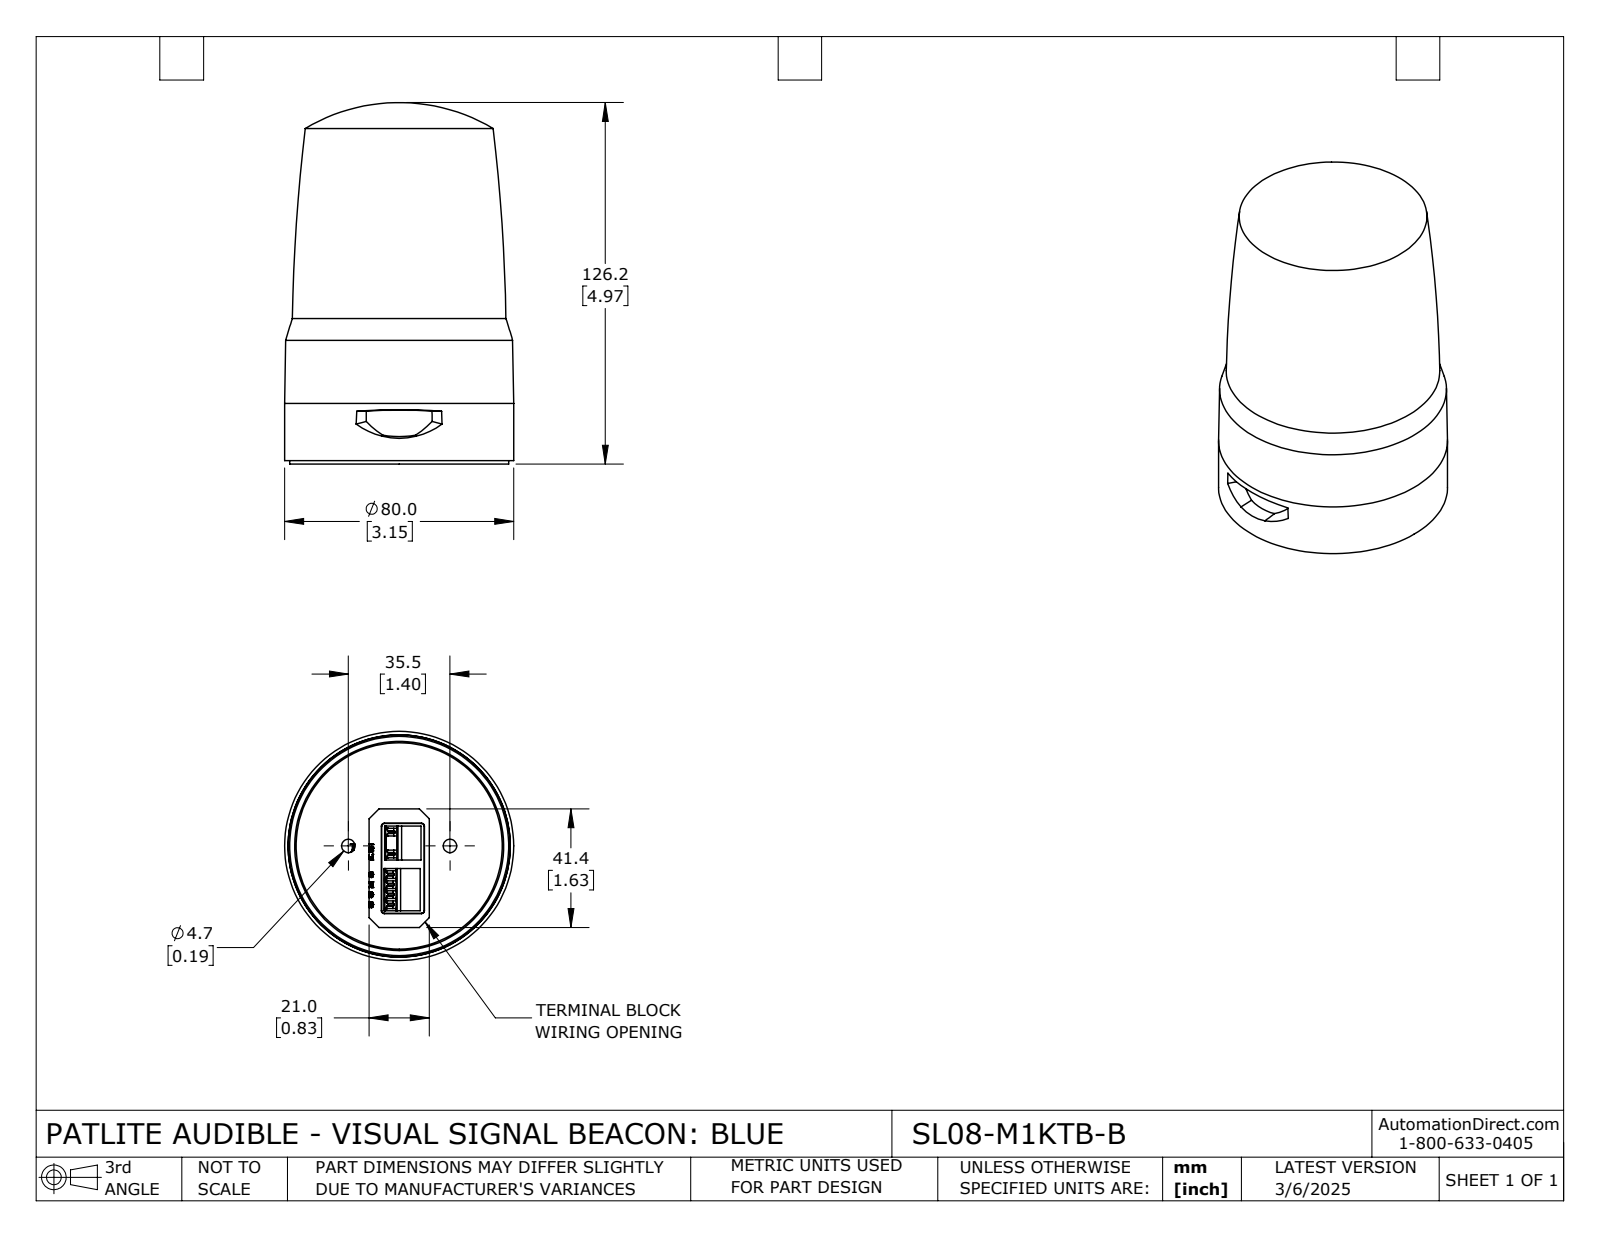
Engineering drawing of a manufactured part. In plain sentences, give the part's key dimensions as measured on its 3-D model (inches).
The part is named "SL08-M1KTB-B". Its 3-D file was written by "SolidWorks 2024 (CONFIG_CONTROL_DESIGN)". It is 2 solids with 635 faces: 370 planar, 32 cylindrical and 233 other. Overall it measures 4.969 by 3.15 by 3.15 inches. Its volume is 29.79 cubic inches and its surface area 84.67 square inches. Round holes: 2 of diameter 0.185, 2 of diameter 0.48, 1 of diameter 2.874. Round bosses or shafts: 1 of diameter 3.15, 1 of diameter 3.012, 1 of diameter 2.937, 1 of diameter 2.835. Partial cylindrical surfaces (rounded edges, fillets, slot ends): 4 of radius 0.039, 2 of radius 0.012, 1 of radius 1.362, 1 of radius 1.378. The main face-to-face distances are 0.618, 0.248, 0.37, 0.118, 0.201, 0.571, 0.124, 0.242, 0.051, 0.49. The hole center spacings are 0.699, 1.398.
